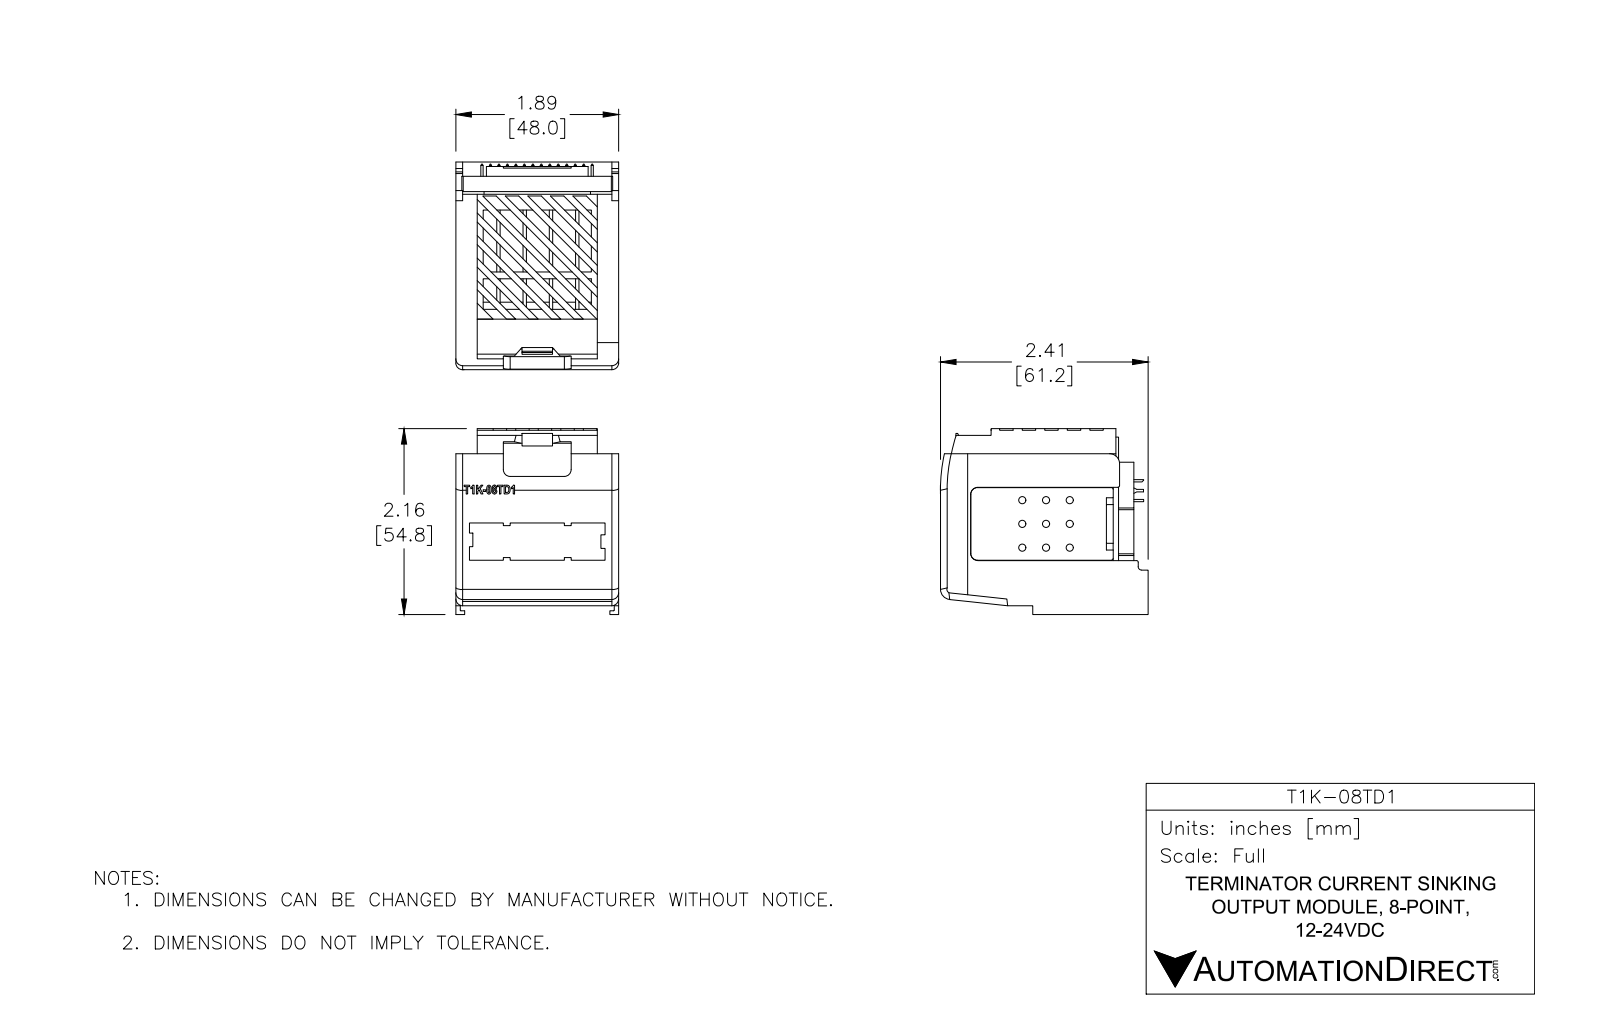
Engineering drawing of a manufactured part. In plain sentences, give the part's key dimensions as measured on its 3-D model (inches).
The part is named "T1K-08TD1". Its 3-D file was written by "SolidWorks 2013 (AUTOMOTIVE_DESIGN)". It is 1 solid with 549 faces: 415 planar, 101 cylindrical and 33 other. Overall it measures 2.563 by 2.416 by 1.874 inches. Its volume is 1.848 cubic inches and its surface area 55.71 square inches. Round holes: 8 of diameter 0.118. Round bosses or shafts: 28 of diameter 0.028. Partial cylindrical surfaces (rounded edges, fillets, slot ends): 10 of radius 0.138, 5 of radius 0.039, 3 of radius 0.01, 3 of radius 0.022, 2 of radius 0.059, 1 of radius 0.315, 1 of radius 0.394, 1 of radius 0.709. The main face-to-face distances are 0.079, 1.795, 1.874, 1.717, 2.179, 1.965, 0.258, 1.537, 2.354, 0.39. The hole center spacings are 0.205, 0.409, 0.614, 0.819, 1.024, 1.228, 1.433.
